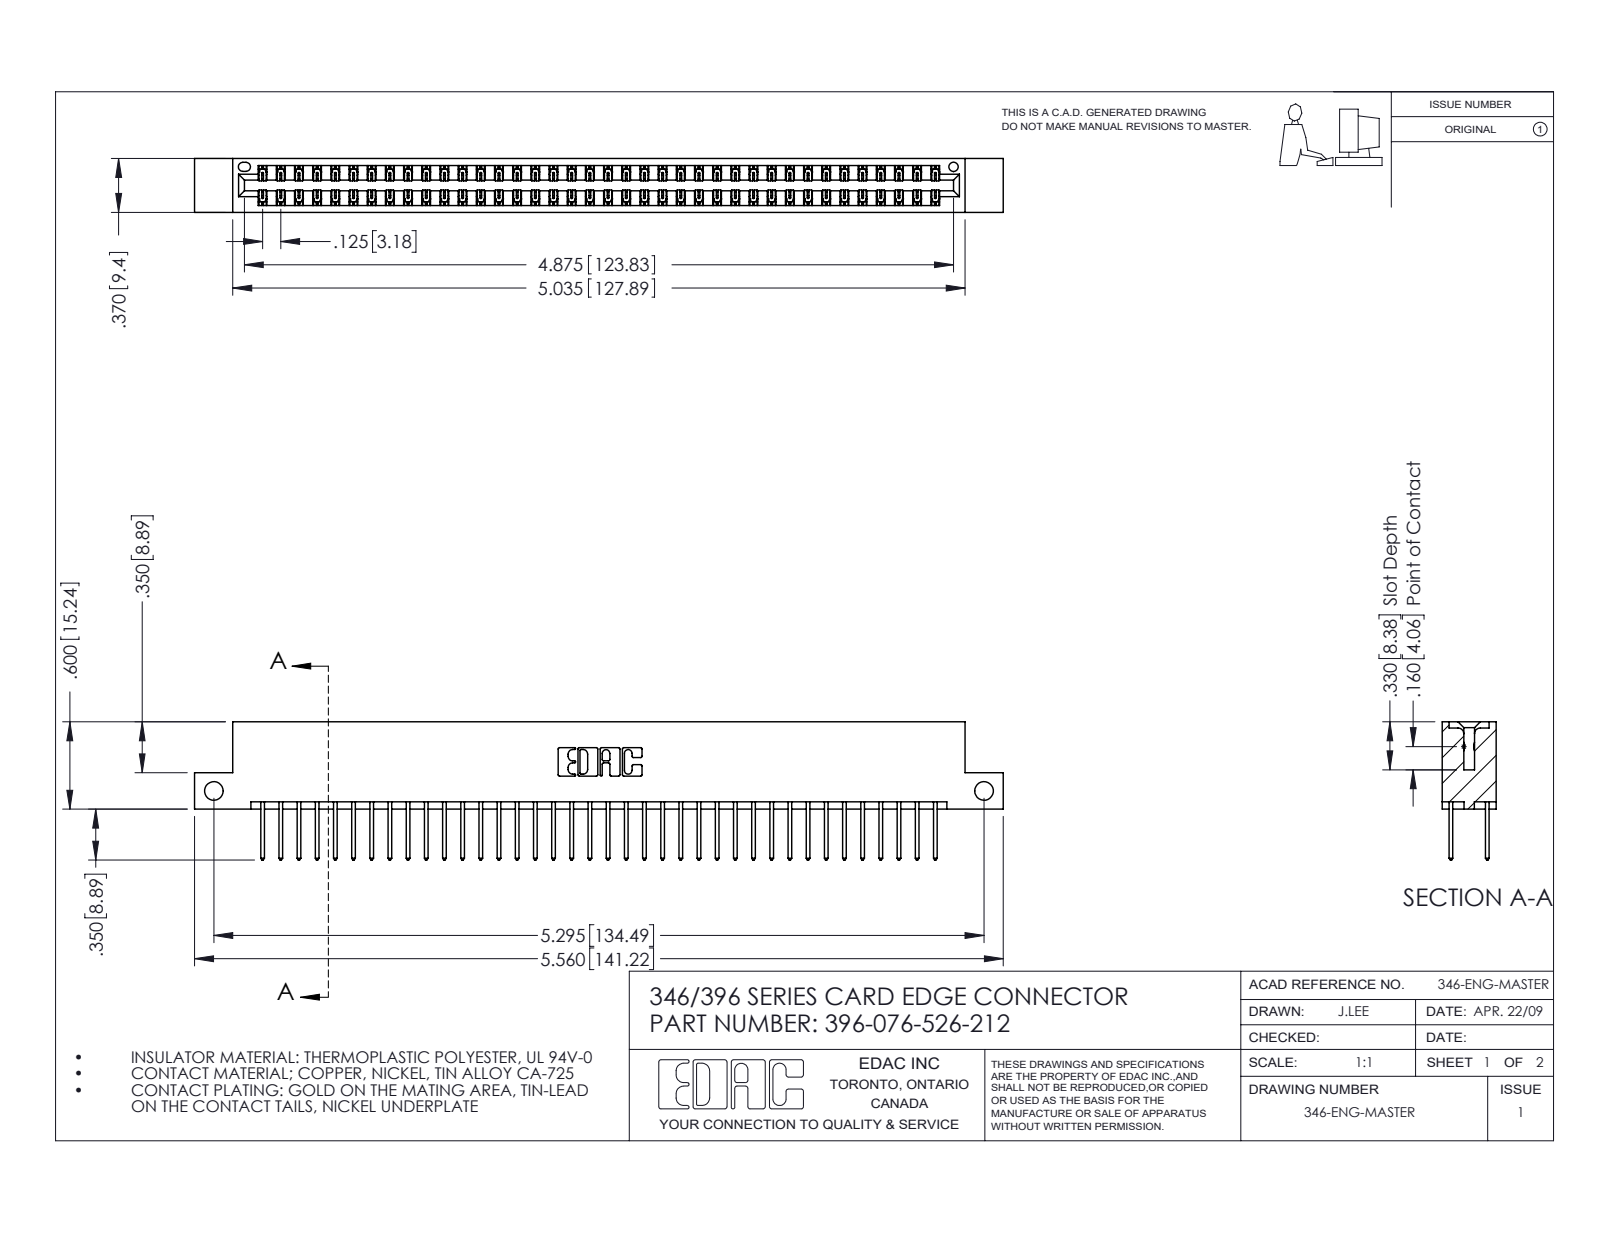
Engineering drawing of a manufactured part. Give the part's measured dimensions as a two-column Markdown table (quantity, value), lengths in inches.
| quantity | value |
| --- | --- |
| part name | 346 Part_Flush Mounting Lugs - Side Mount; 396-076-526-212; 345-292-001_345-293-126 |
| STEP written by | SolidWorks 2016 (CONFIG_CONTROL_DESIGN) |
| units | inches |
| bodies | 77 solids, 4074 faces (2736 planar, 1338 cylindrical, 0 other) |
| overall size | 5.56 × 0.95 × 0.37 |
| volume | 0.841 in³ |
| surface area | 29.91 in² |
| round holes (diameter × count) | 0.128 × 2, 0.064 × 1 |
| partial cylindrical surfaces (radius × count) | 0.006 × 114, 0.01 × 76, 0.01 × 22, 0.007 × 6, 0.031 × 6, 0.026 × 3, 0.014 × 2, 0.022 × 2 |
| main face-to-face distances | 0.048, 0.322, 0.25, 0.37, 0.072, 0.298, 0.025, 0.275, 0.148, 0.222 |
| hole center spacings | 5.295 |
